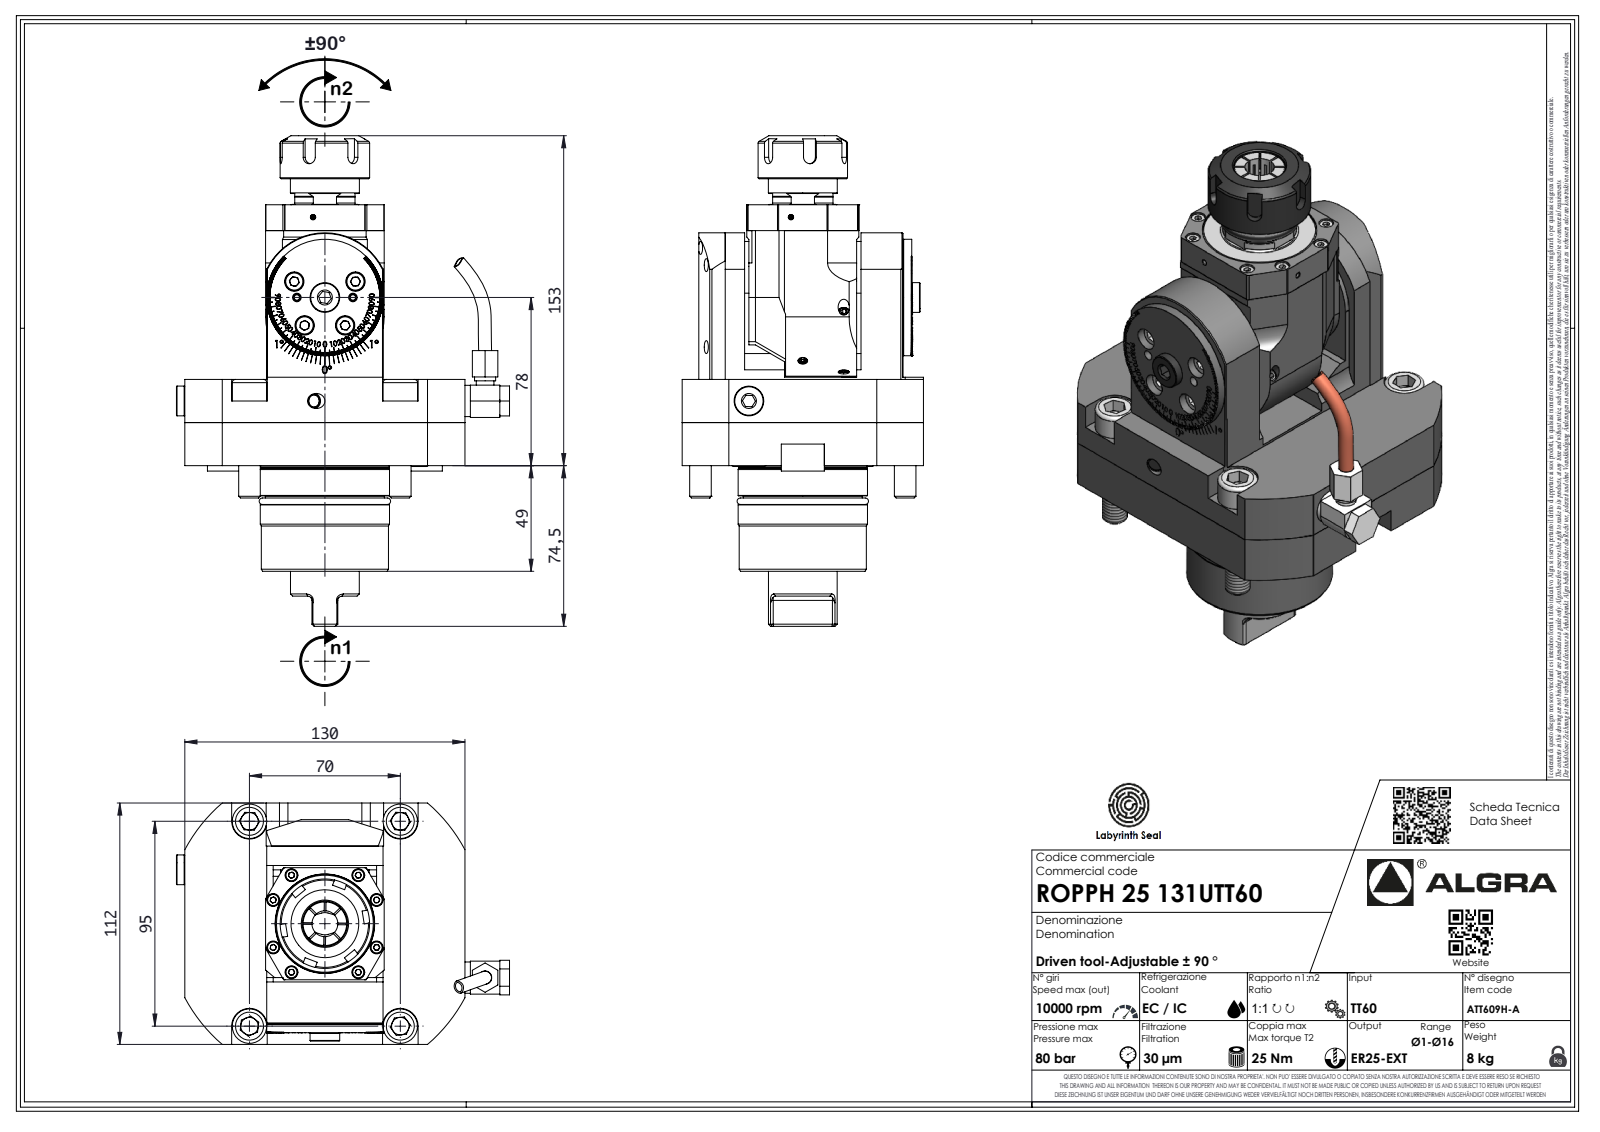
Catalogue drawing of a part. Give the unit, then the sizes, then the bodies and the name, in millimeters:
Units: millimetres
Overall size (bounding box): 227.53 × 150.7 × 112
Round holes (diameter × count): ⌀2.1 ×1
Round bosses / shafts (diameter × count): ⌀60 ×1, ⌀59.8 ×1, ⌀59 ×1, ⌀55.2 ×1, ⌀54 ×1, ⌀41.5 ×1, ⌀32 ×1, ⌀31.9 ×1
Partial cylindrical surfaces — rounded edges, fillets, slot ends (radius × count): R2 ×14, R1 ×8, R0.33 ×7, R0.52 ×7, R3.7 ×7, R10 ×6, R3 ×5, R5 ×4
Main face-to-face distances: 40, 1, 38, 92, 54.5, 0.5, 81, 37.5, 41, 54
Volume: 1 077 000 mm³ · Surface area: 100 700 mm²
Bodies: 1 solid, 647 faces (412 planar, 118 cylindrical, 117 other)
Part name (STEP PRODUCT): ROPPH25131UTT60
STEP written by: SolidWorks 2023 (AUTOMOTIVE_DESIGN)
